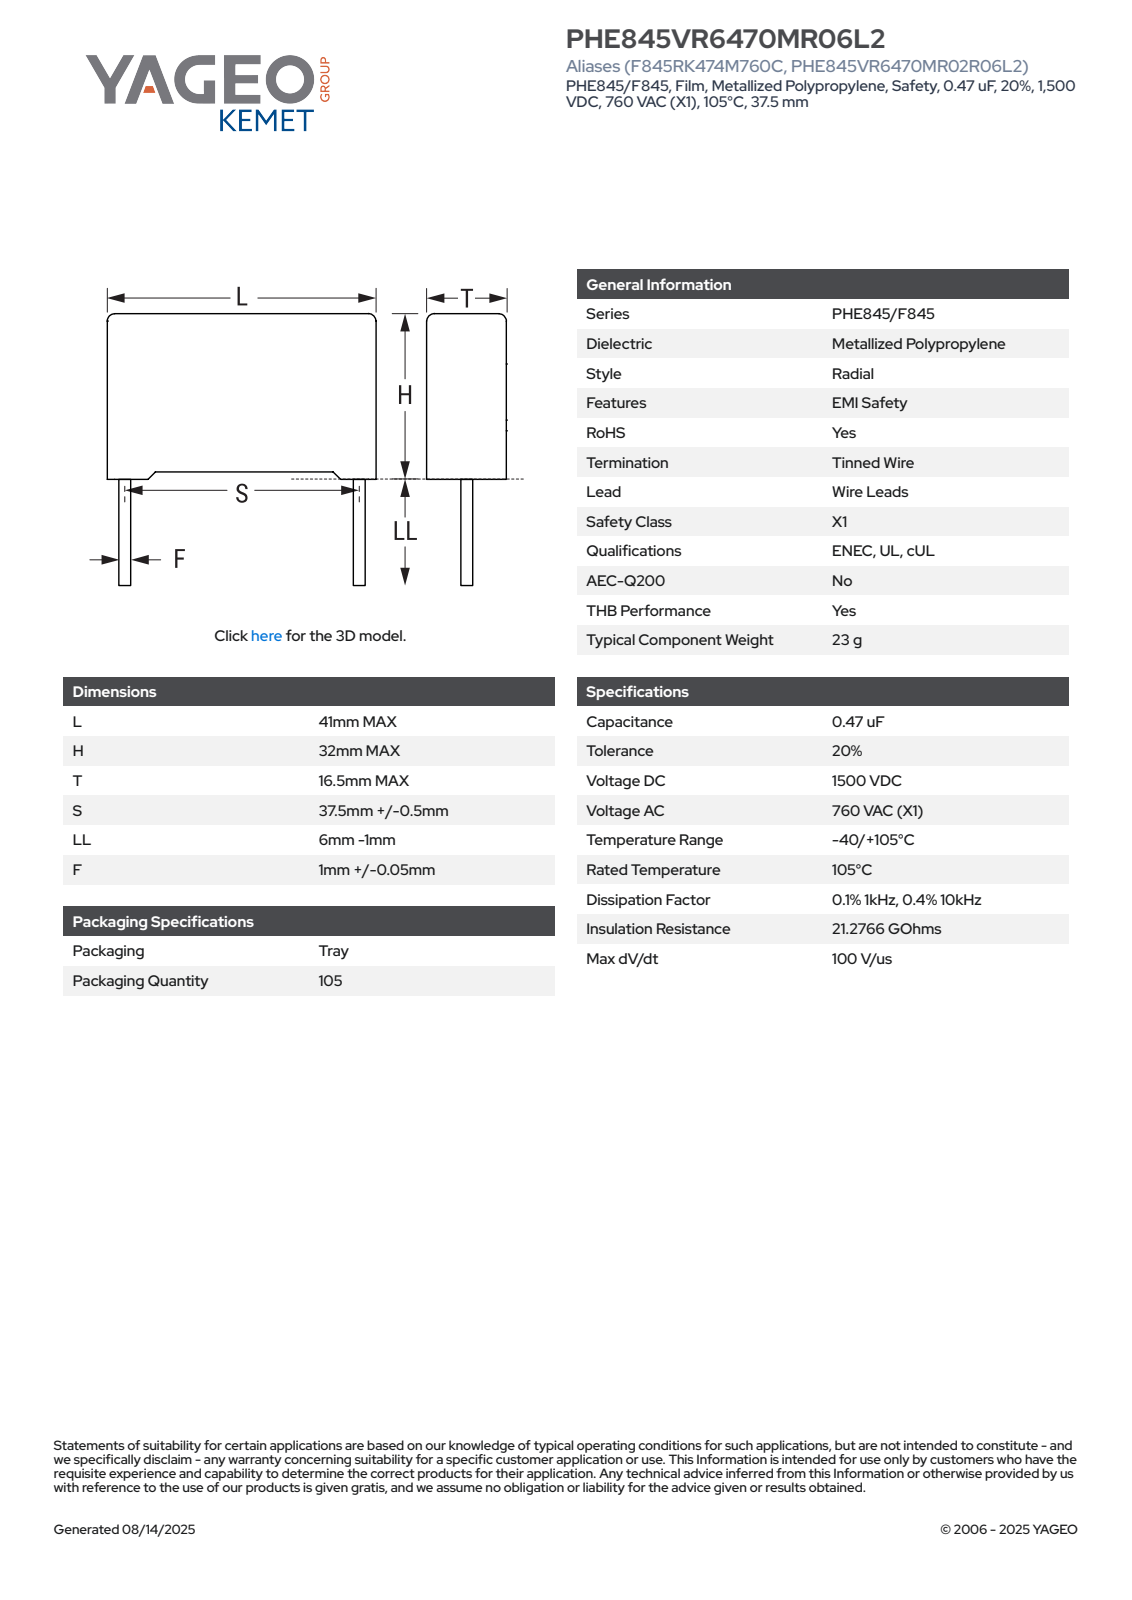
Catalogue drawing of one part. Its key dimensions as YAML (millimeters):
part_name: "CFR_RB2_41X32X16.5_L41H32T16.5S37.5LL5F1.05"
step_written_by: "SolidWorks 2021 (AUTOMOTIVE_DESIGN)"
units: millimeters
bodies: {solids: 4, faces: 87, planar: 79, cylindrical: 8, other: 0}
overall_size: [41, 37, 16.5]
volume: 20998
surface_area: 5130
round_bosses_or_shafts:
  - {diameter: 1.05, count: 2}
partial_cylinders:
  - {radius: 0.5, count: 4}
face_to_face_distances: [16.5, 30.9, 41, 0.35, 31.25, 0.75, 1.1, 32, 16.51, 1.37]
